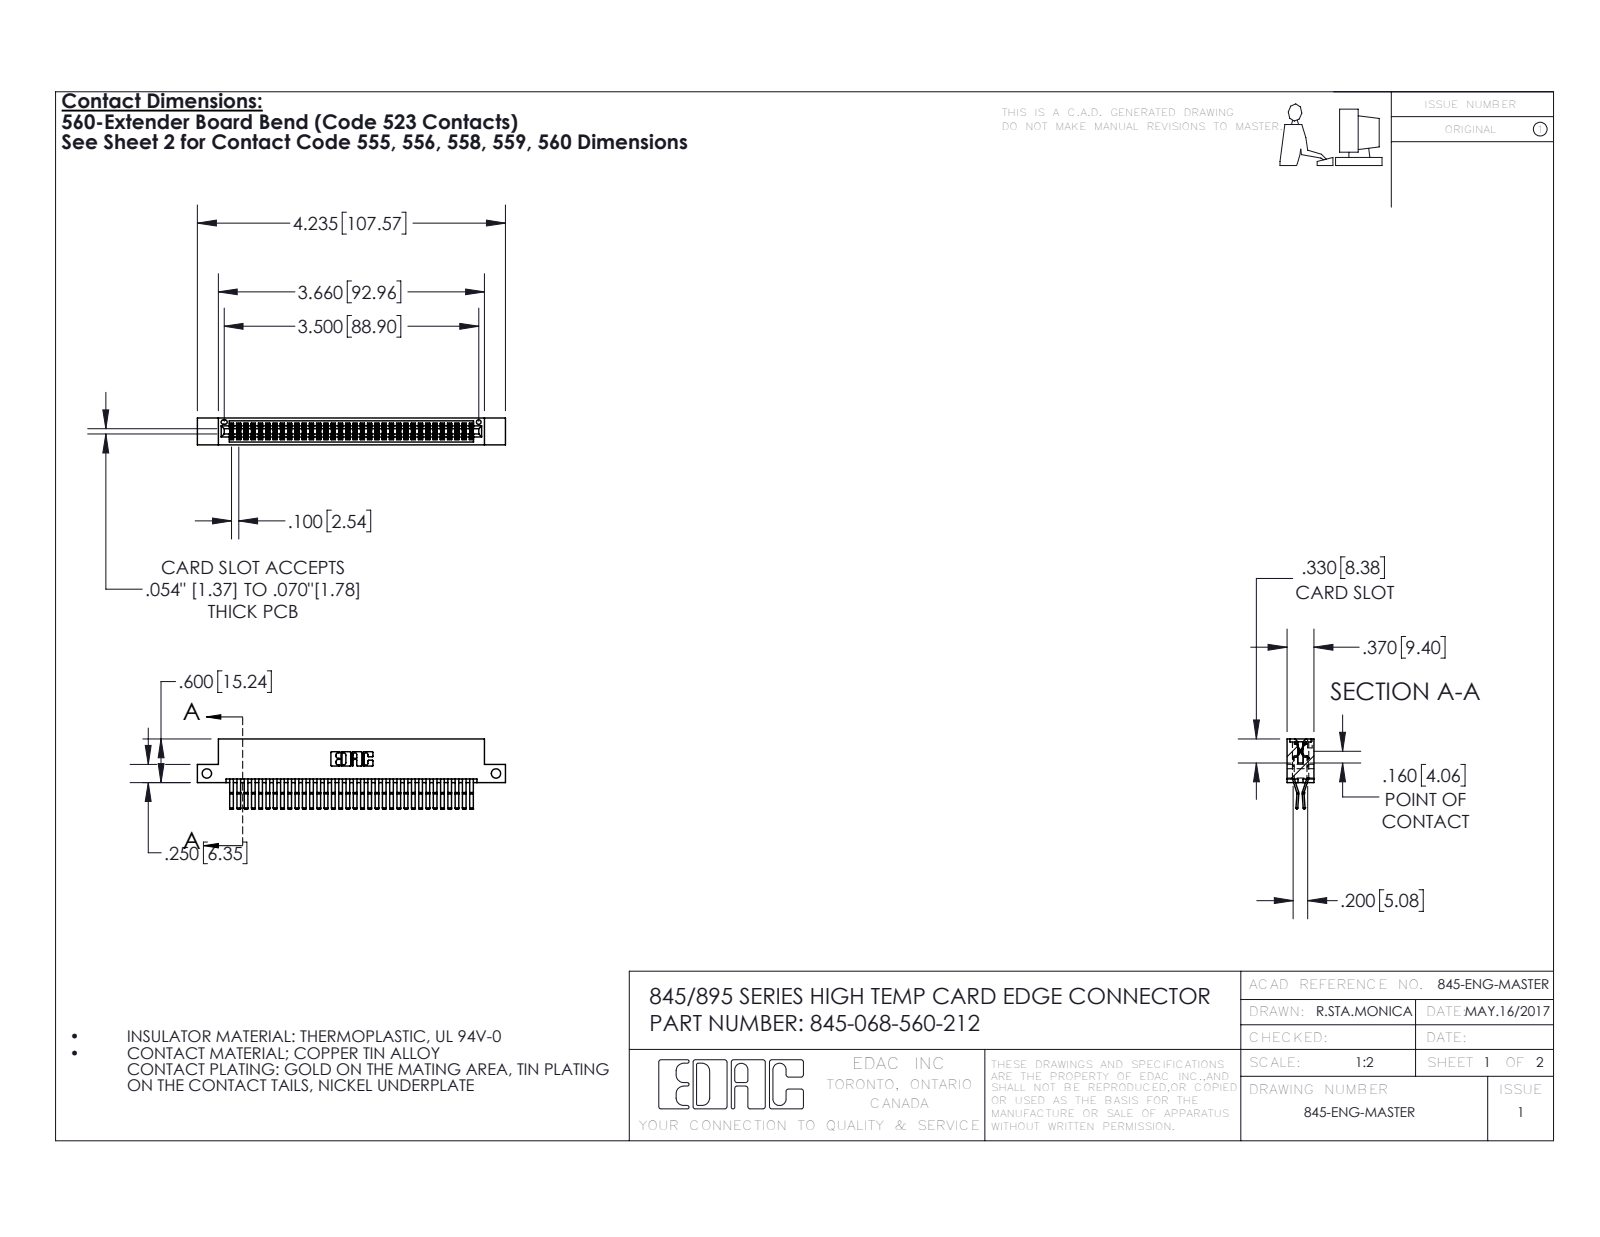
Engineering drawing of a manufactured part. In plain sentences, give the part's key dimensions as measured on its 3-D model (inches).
The part is named "345-292-001_560 Tail; 345 Part_Flush Mounting Lugs - Side Mount; 345-068-560-212". Its 3-D file was written by "SolidWorks 2016 (CONFIG_CONTROL_DESIGN)". It is 69 solids with 3662 faces: 2324 planar, 1338 cylindrical and 0 other. Overall it measures 4.235 by 0.962 by 0.37 inches. Its volume is 0.655 cubic inches and its surface area 25.92 square inches. Round holes: 2 of diameter 0.128, 1 of diameter 0.064. Partial cylindrical surfaces (rounded edges, fillets, slot ends): 135 of radius 0.006, 22 of radius 0.01, 6 of radius 0.007, 6 of radius 0.031, 3 of radius 0.026, 2 of radius 0.01, 2 of radius 0.014, 2 of radius 0.019. The main face-to-face distances are 0.025, 0.298, 0.072, 0.2, 0.37, 0.098, 0.272, 0.225, 0.175, 0.149. The hole center spacings are 3.975.
